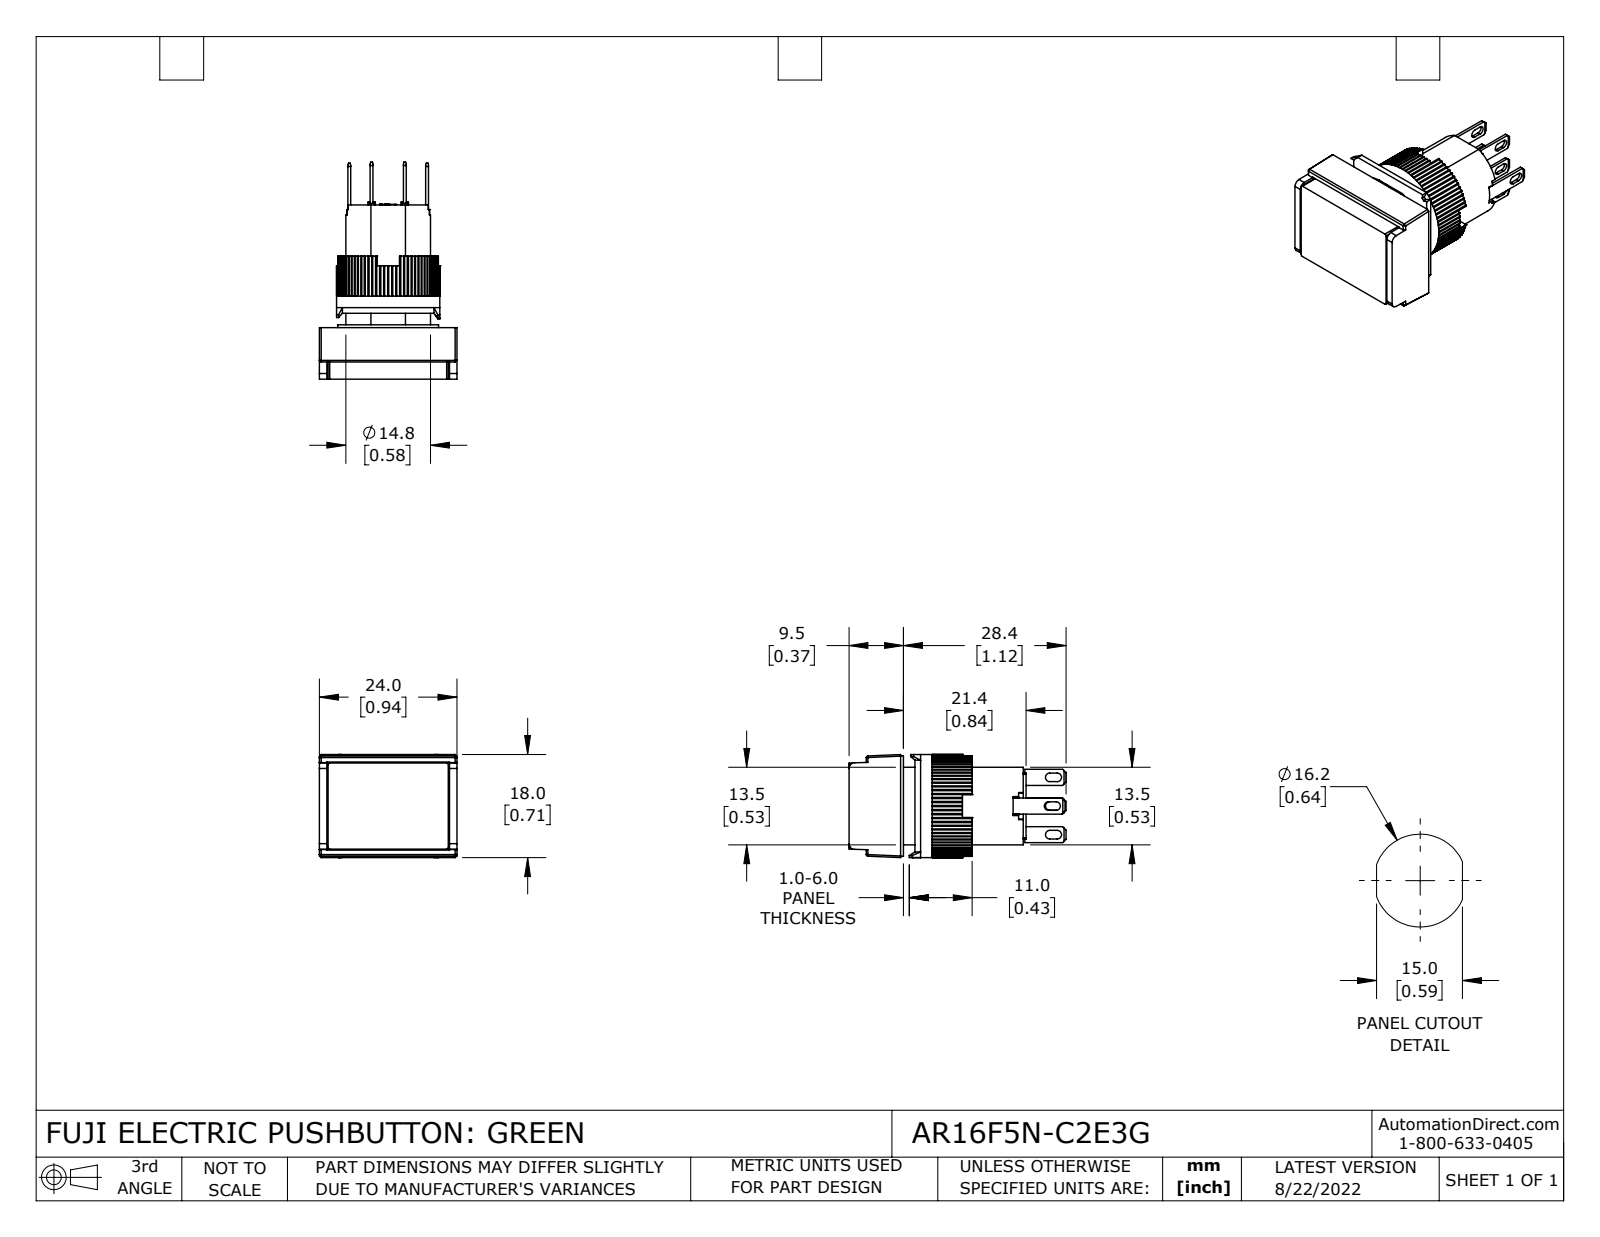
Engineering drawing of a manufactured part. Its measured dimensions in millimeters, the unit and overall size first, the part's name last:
Units: millimetres
Overall size (bounding box): 37.9 × 24 × 18
Round holes (diameter × count): ⌀13.8 ×1, ⌀14.8 ×1
Round bosses / shafts (diameter × count): ⌀18 ×1, ⌀17.6 ×1
Partial cylindrical surfaces — rounded edges, fillets, slot ends (radius × count): R0.3 ×80, R0.2 ×12, R0.8 ×8, R0.3 ×6, R1 ×2
Main face-to-face distances: 5.4, 9, 3.6, 8.9, 12.5, 3.5, 0.5, 21.4, 1.5, 11.5
Volume: 7 280 mm³ · Surface area: 6 004 mm²
Bodies: 14 solids, 843 faces (656 planar, 183 cylindrical, 4 other)
Part name (STEP PRODUCT): AR16F5N-C2E3G
STEP written by: SolidWorks 2021 (CONFIG_CONTROL_DESIGN)
